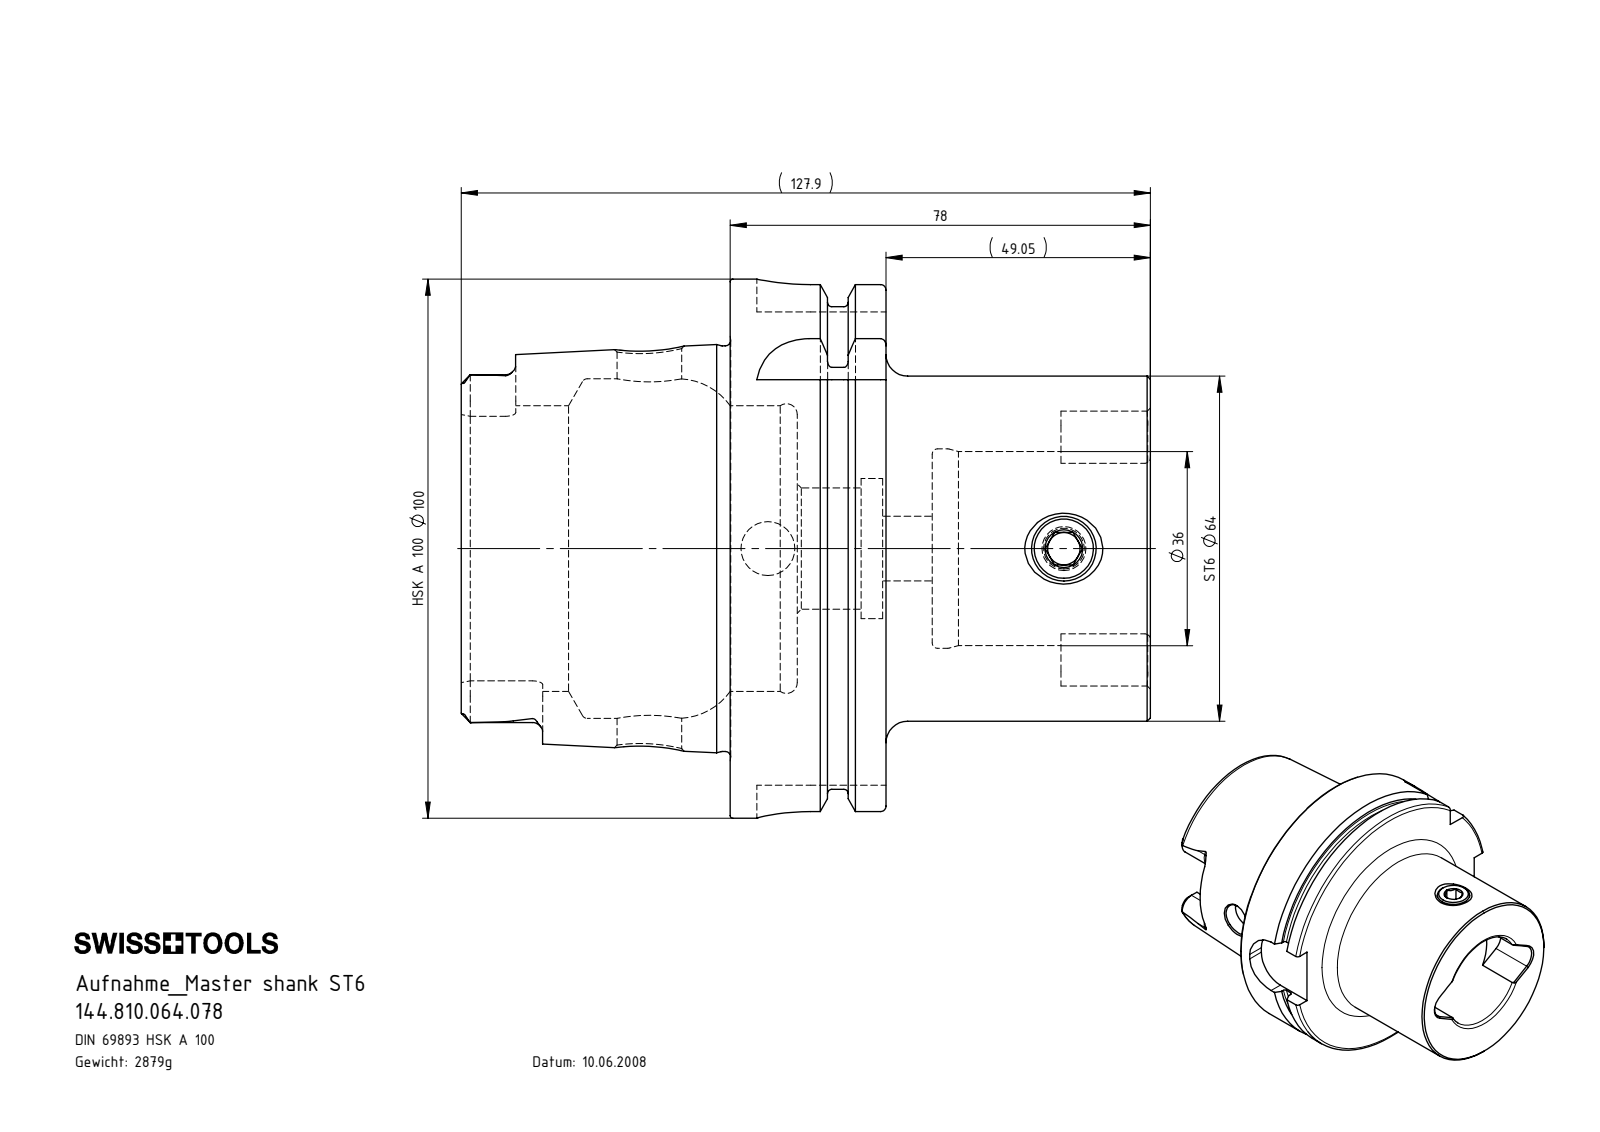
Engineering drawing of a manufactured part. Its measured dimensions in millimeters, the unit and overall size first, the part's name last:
Units: millimetres
Overall size (bounding box): 127.9 × 100 × 100
Round holes (diameter × count): ⌀12 ×2, ⌀6 ×1, ⌀10 ×1, ⌀11 ×1, ⌀22.5 ×1, ⌀26 ×1, ⌀36 ×1, ⌀37 ×1, ⌀53 ×1, ⌀63 ×1
Round bosses / shafts (diameter × count): ⌀100 ×1, ⌀91.95 ×1, ⌀75.26 ×1, ⌀64 ×1, ⌀12 ×1
Partial cylindrical surfaces — rounded edges, fillets, slot ends (radius × count): R1.9 ×6, R4.88 ×4, R10 ×4, R5.2 ×2
Main face-to-face distances: 28.95, 78, 49.05, 12.45, 16.5, 65.55, 49.9, 62.35, 78.85, 127.9
Hole centre spacings: 54.95
Volume: 366 790 mm³ · Surface area: 65 313 mm²
Bodies: 2 solids, 208 faces (63 planar, 59 cylindrical, 86 other)
Part name (STEP PRODUCT): ST6-ER1.001.018_A; HA0-ST6.K01.078_B_Fertigbearbeitung; HA0-ST6.K01.078
STEP written by: SolidWorks 2015 (AUTOMOTIVE_DESIGN)
